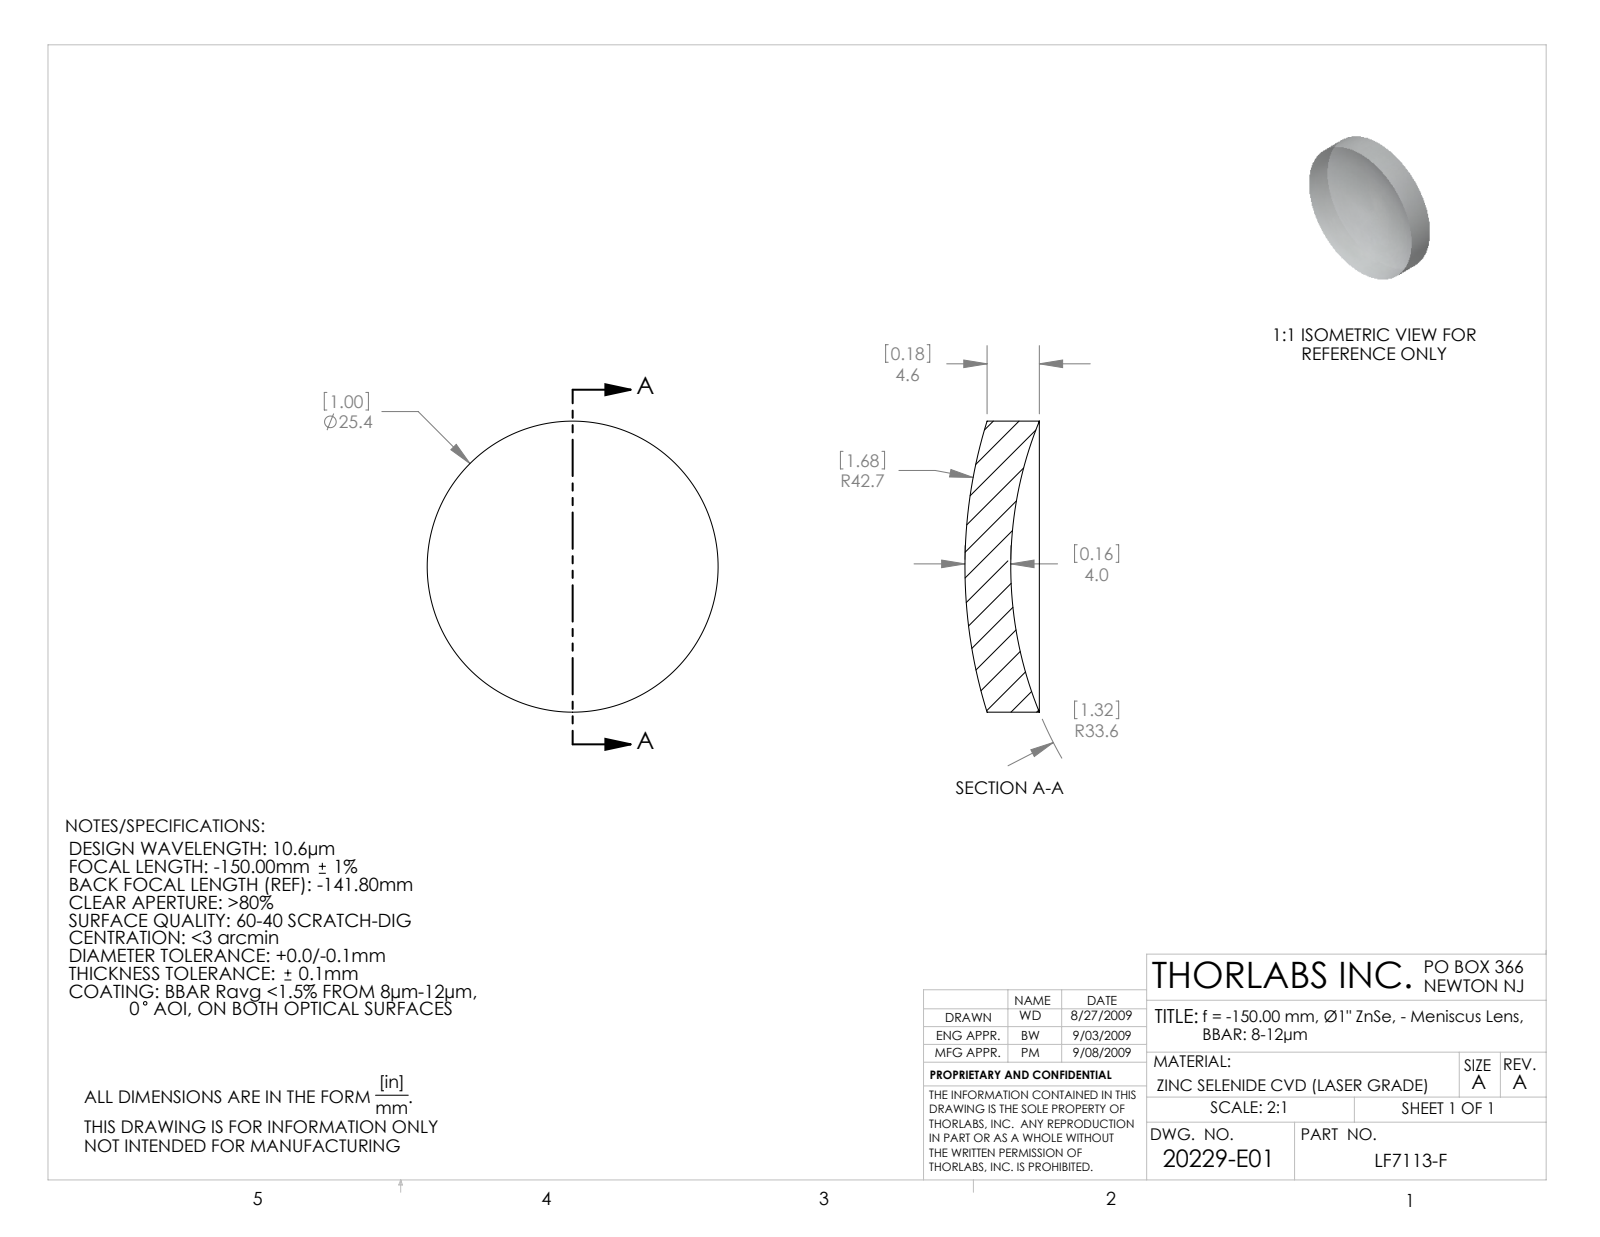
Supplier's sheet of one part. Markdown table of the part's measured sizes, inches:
| quantity | value |
| --- | --- |
| part name | 20229-E0W |
| STEP written by | SolidWorks 2007 (CONFIG_CONTROL_DESIGN) |
| units | inches |
| bodies | 1 solid, 6 faces (0 planar, 2 cylindrical, 4 other) |
| overall size | 1 × 1 × 0.256 |
| volume | 0.132 in³ |
| surface area | 2.184 in² |
| round bosses / shafts (diameter × count) | 1 × 1 |
